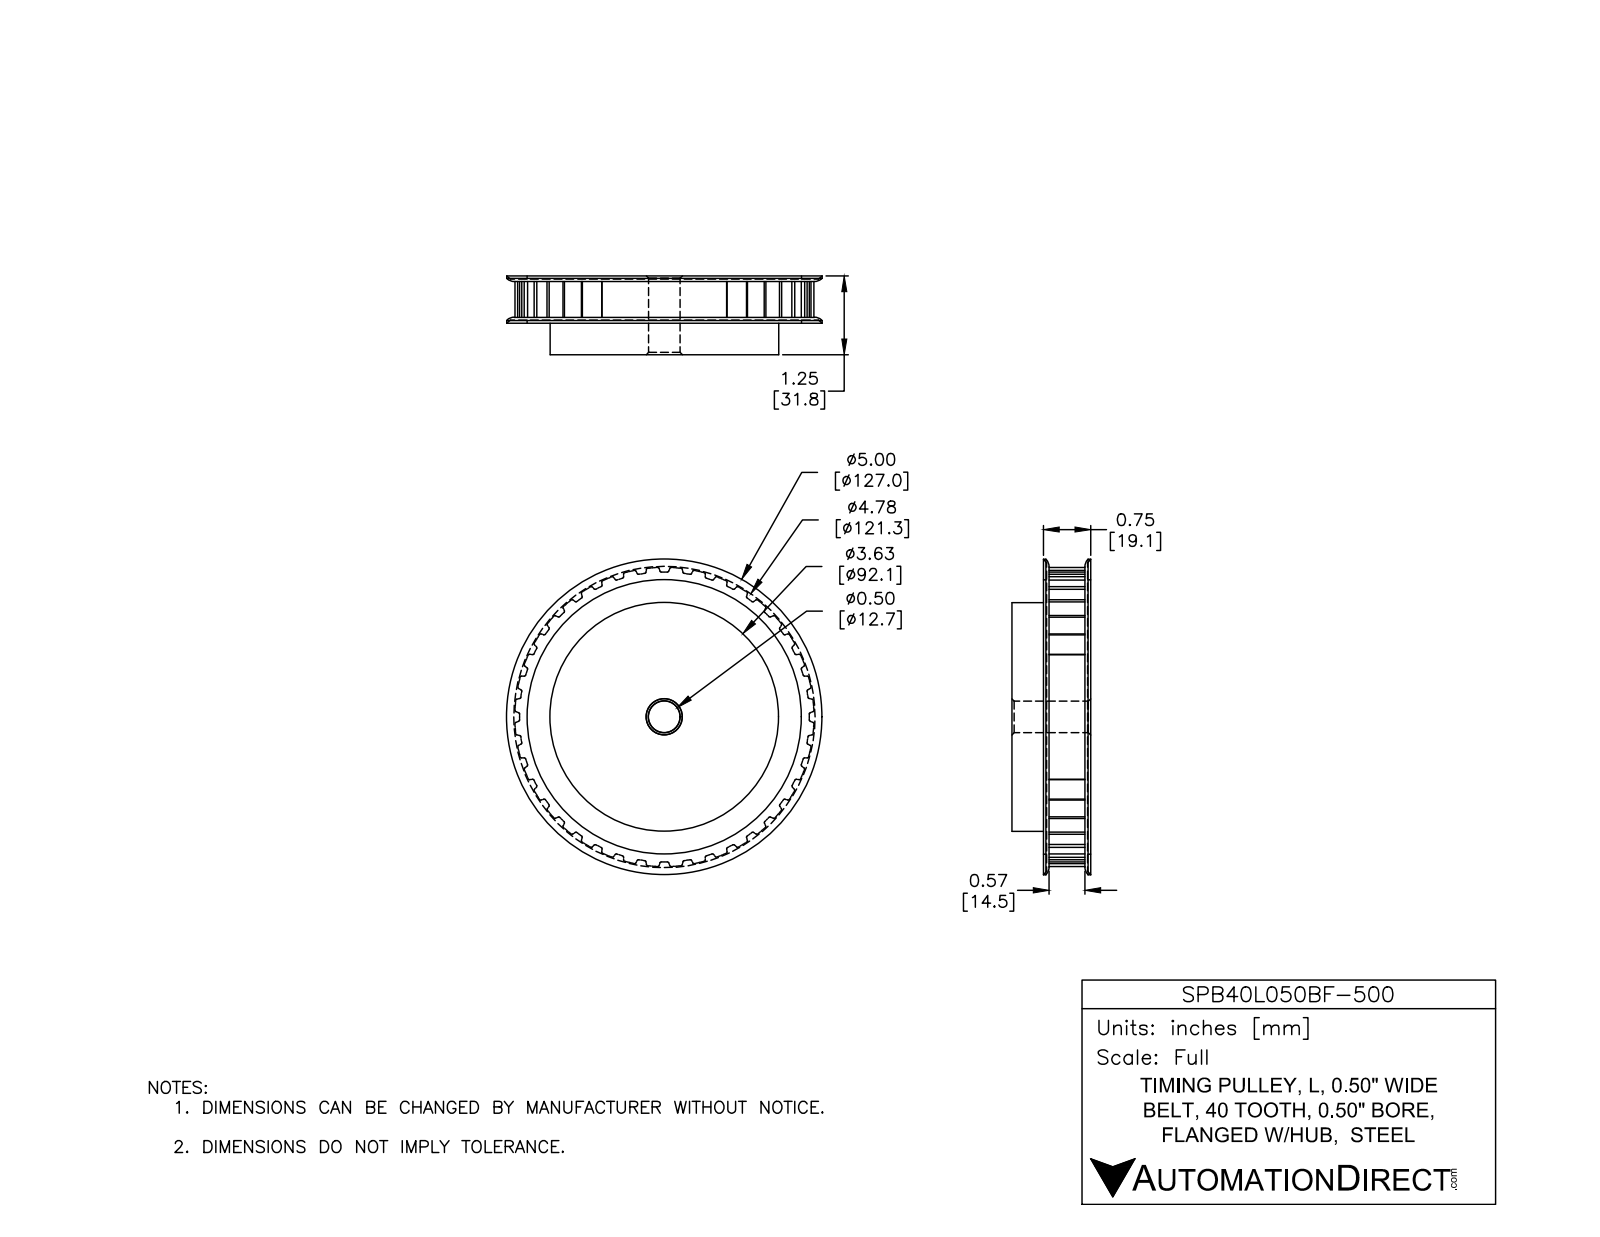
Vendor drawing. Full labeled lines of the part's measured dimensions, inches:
Part name (STEP PRODUCT): SPB40L050BF-500
STEP written by: SolidWorks 2015 (AUTOMOTIVE_DESIGN)
Units: inches
Bodies: 1 solid, 385 faces (127 planar, 242 cylindrical, 16 other)
Overall size (bounding box): 5 × 5 × 1.25
Volume: 17.77 in³ · Surface area: 65.42 in²
Round holes (diameter × count): ⌀0.5 ×1
Round bosses / shafts (diameter × count): ⌀5 ×1, ⌀4.35 ×1, ⌀3.625 ×1
Partial cylindrical surfaces — rounded edges, fillets, slot ends (radius × count): R0.02 ×160, R2.372 ×1, R2.373 ×1
Main face-to-face distances: 1.25, 0.05, 0.7, 0.75, 0.5, 0.65, 1.2, 0.55, 0.09, 0.66
